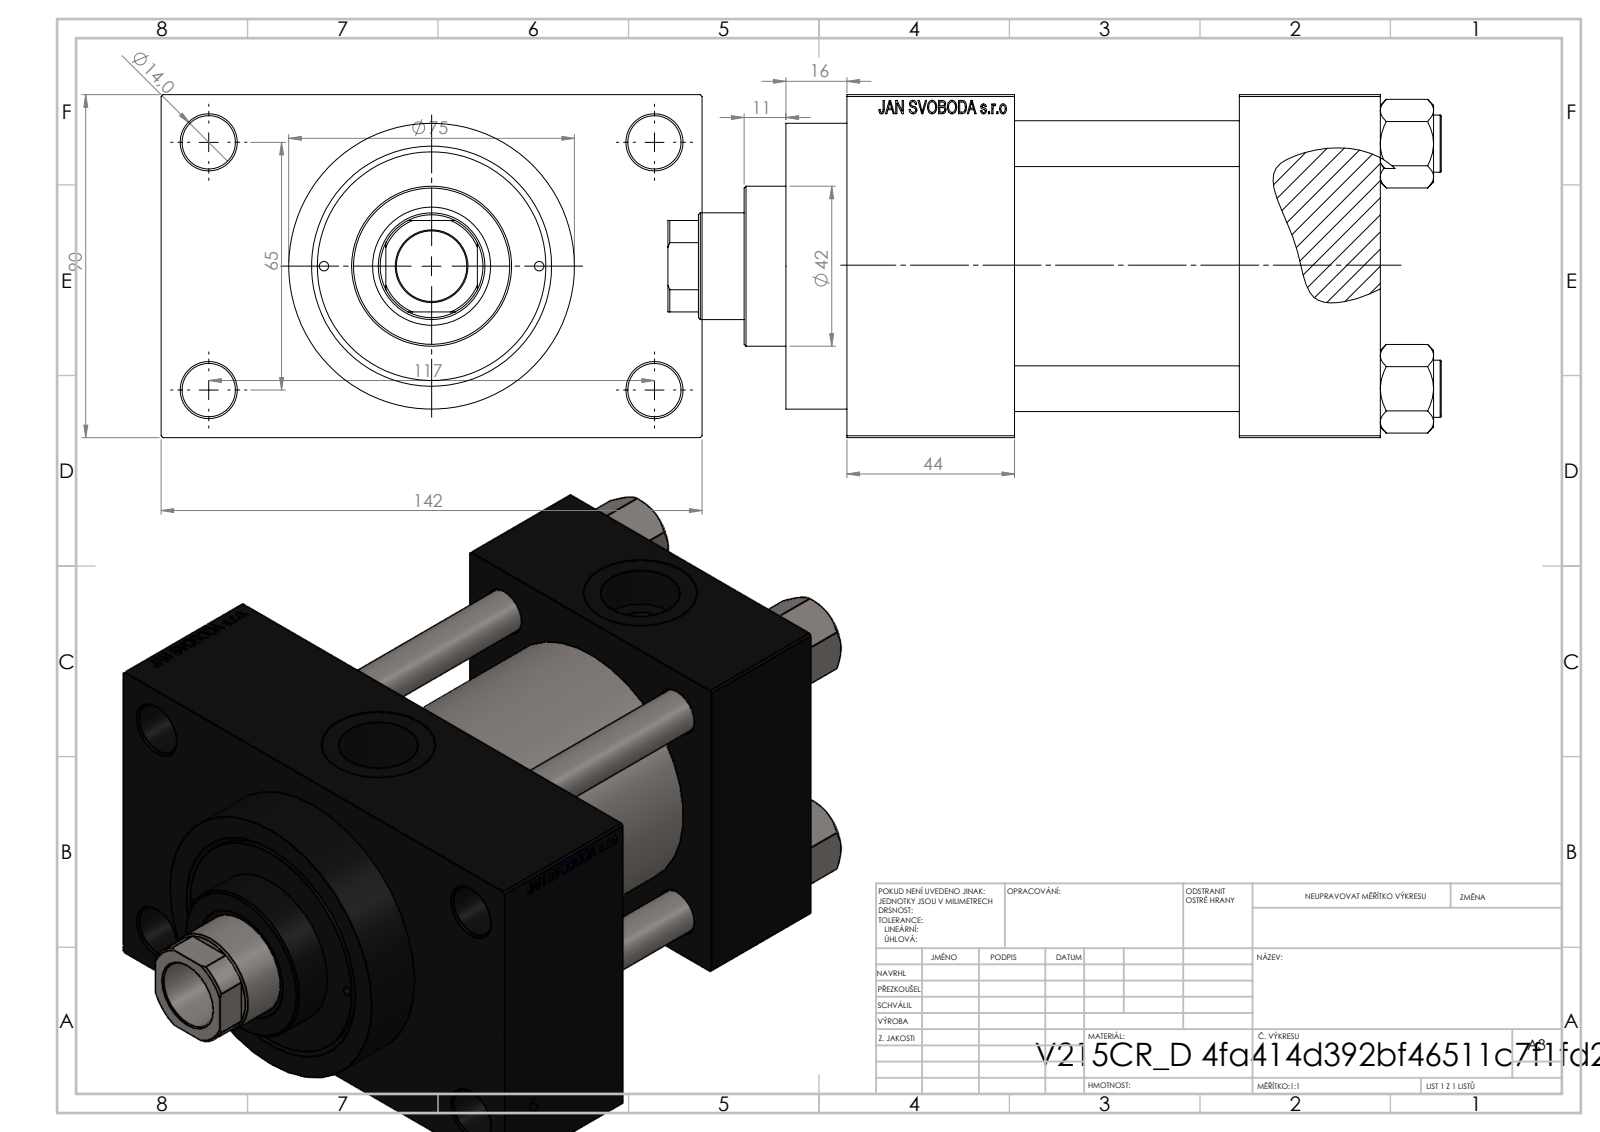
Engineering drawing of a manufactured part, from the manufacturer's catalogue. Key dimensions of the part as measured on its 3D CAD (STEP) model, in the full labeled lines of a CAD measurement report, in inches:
Part name (STEP PRODUCT): V215_VC_A; V215CR_D_TYCINKA; V215CR_VCP_D; NUT_M5_D (+1 more)
STEP written by: SolidWorks 2019 (CONFIG_CONTROL_DESIGN)
Units: inches
Bodies: 11 solids, 1112 faces (499 planar, 93 cylindrical, 520 other)
Overall size (bounding box): 7.992 × 5.591 × 3.543
Volume: 67.43 in³ · Surface area: 307.7 in²
Round holes (diameter × count): ⌀0.472 ×4, ⌀0.551 ×4, ⌀0.098 ×2, ⌀0.276 ×2, ⌀0.825 ×2, ⌀1.181 ×2, ⌀0.728 ×1, ⌀1.102 ×1, ⌀1.22 ×1, ⌀1.969 ×1, ⌀2.362 ×1, ⌀2.48 ×1
Round bosses / shafts (diameter × count): ⌀0.591 ×4, ⌀2.953 ×1, ⌀2.717 ×1, ⌀1.654 ×1
Partial cylindrical surfaces — rounded edges, fillets, slot ends (radius × count): R0.531 ×1
Main face-to-face distances: 3.543, 2.323, 1.457, 3.78, 5.512, 4.055, 1.732, 1.024, 4.567, 5.591
Hole centre spacings: 1.037, 1.275, 1.748, 1.79, 2.531, 2.635, 2.694, 2.748
